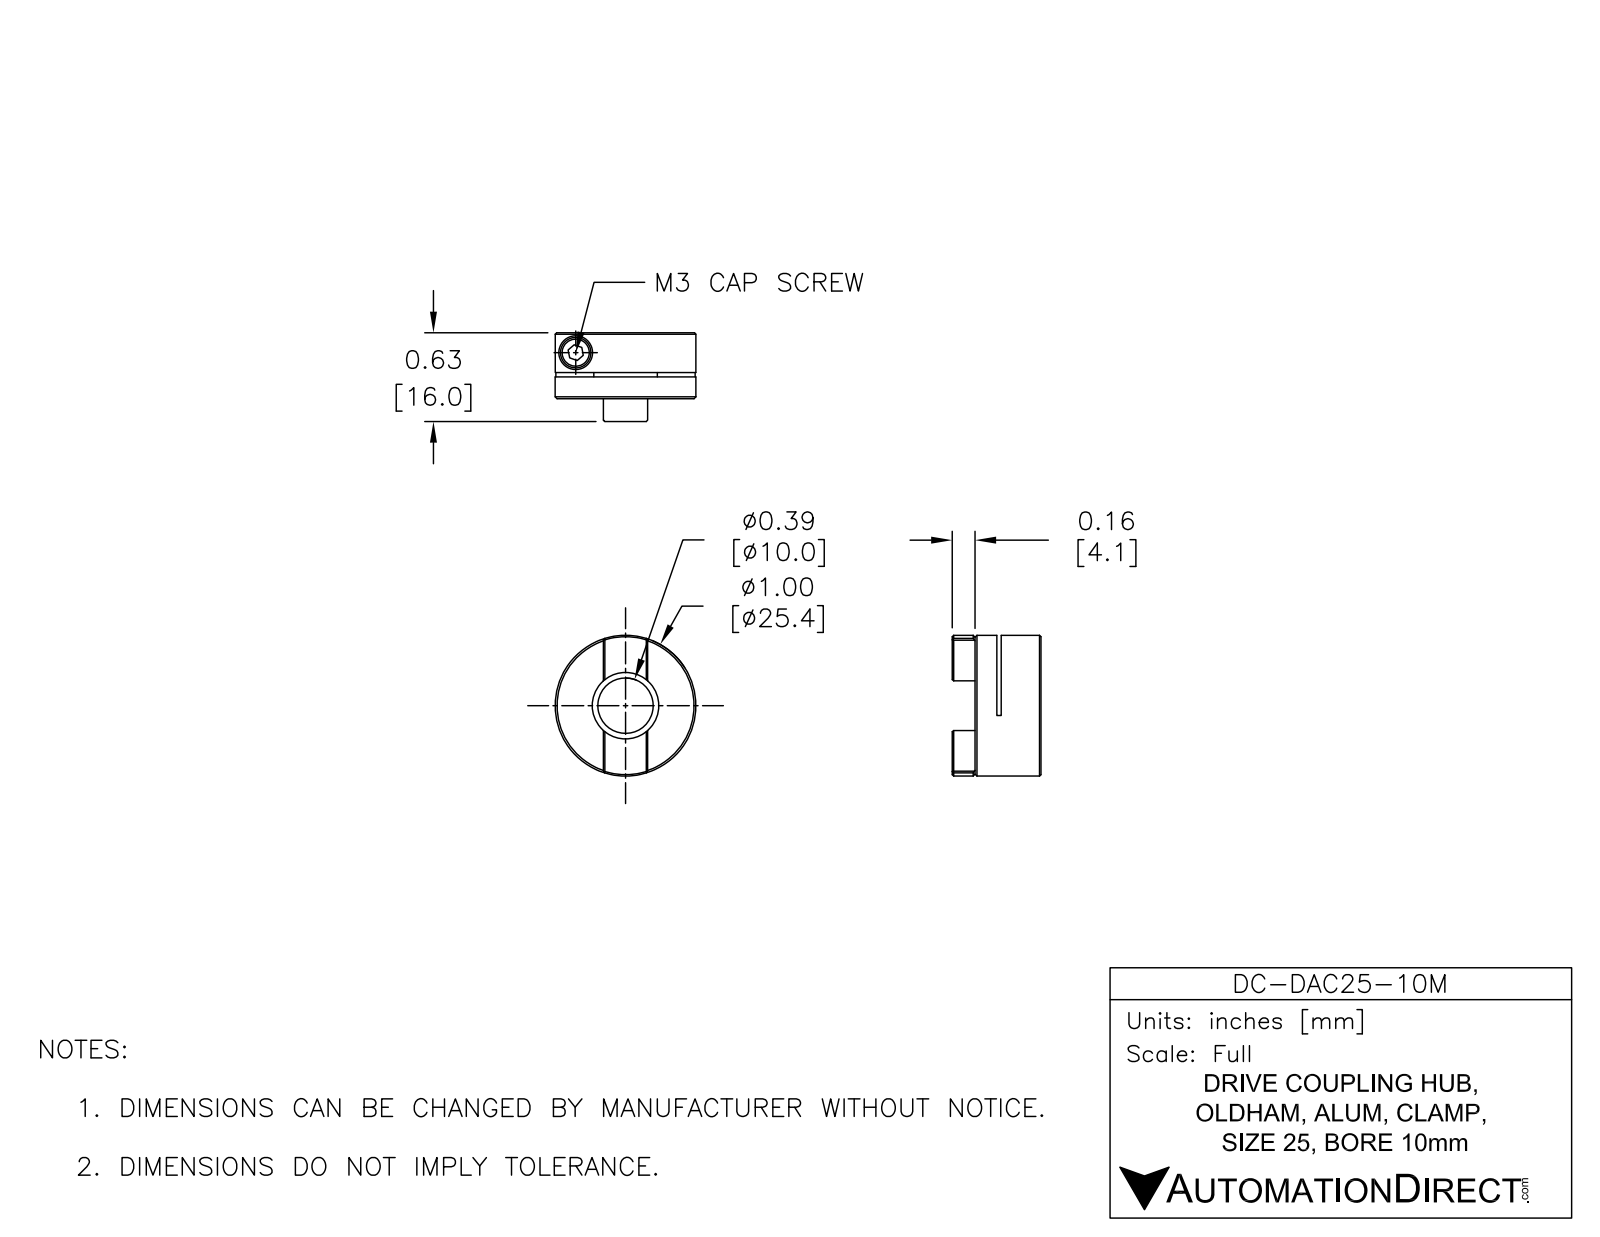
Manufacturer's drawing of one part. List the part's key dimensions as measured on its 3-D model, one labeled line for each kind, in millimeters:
Part name (STEP PRODUCT): DC-DAC25-10M
STEP written by: SolidWorks 2015 (AUTOMOTIVE_DESIGN)
Units: millimetres
Bodies: 1 solid, 52 faces (29 planar, 15 cylindrical, 8 other)
Overall size (bounding box): 25.4 × 25.4 × 16
Volume: 5 083 mm³ · Surface area: 3 145 mm²
Round holes (diameter × count): ⌀2.46 ×1, ⌀3.4 ×1, ⌀6.1 ×1, ⌀10 ×1
Round bosses / shafts (diameter × count): ⌀25.4 ×1
Partial cylindrical surfaces — rounded edges, fillets, slot ends (radius × count): R25.4 ×1
Main face-to-face distances: 11.89, 7.95, 3.94, 7.16, 0.79, 4.73, 16, 8.84, 8.05, 4.11
